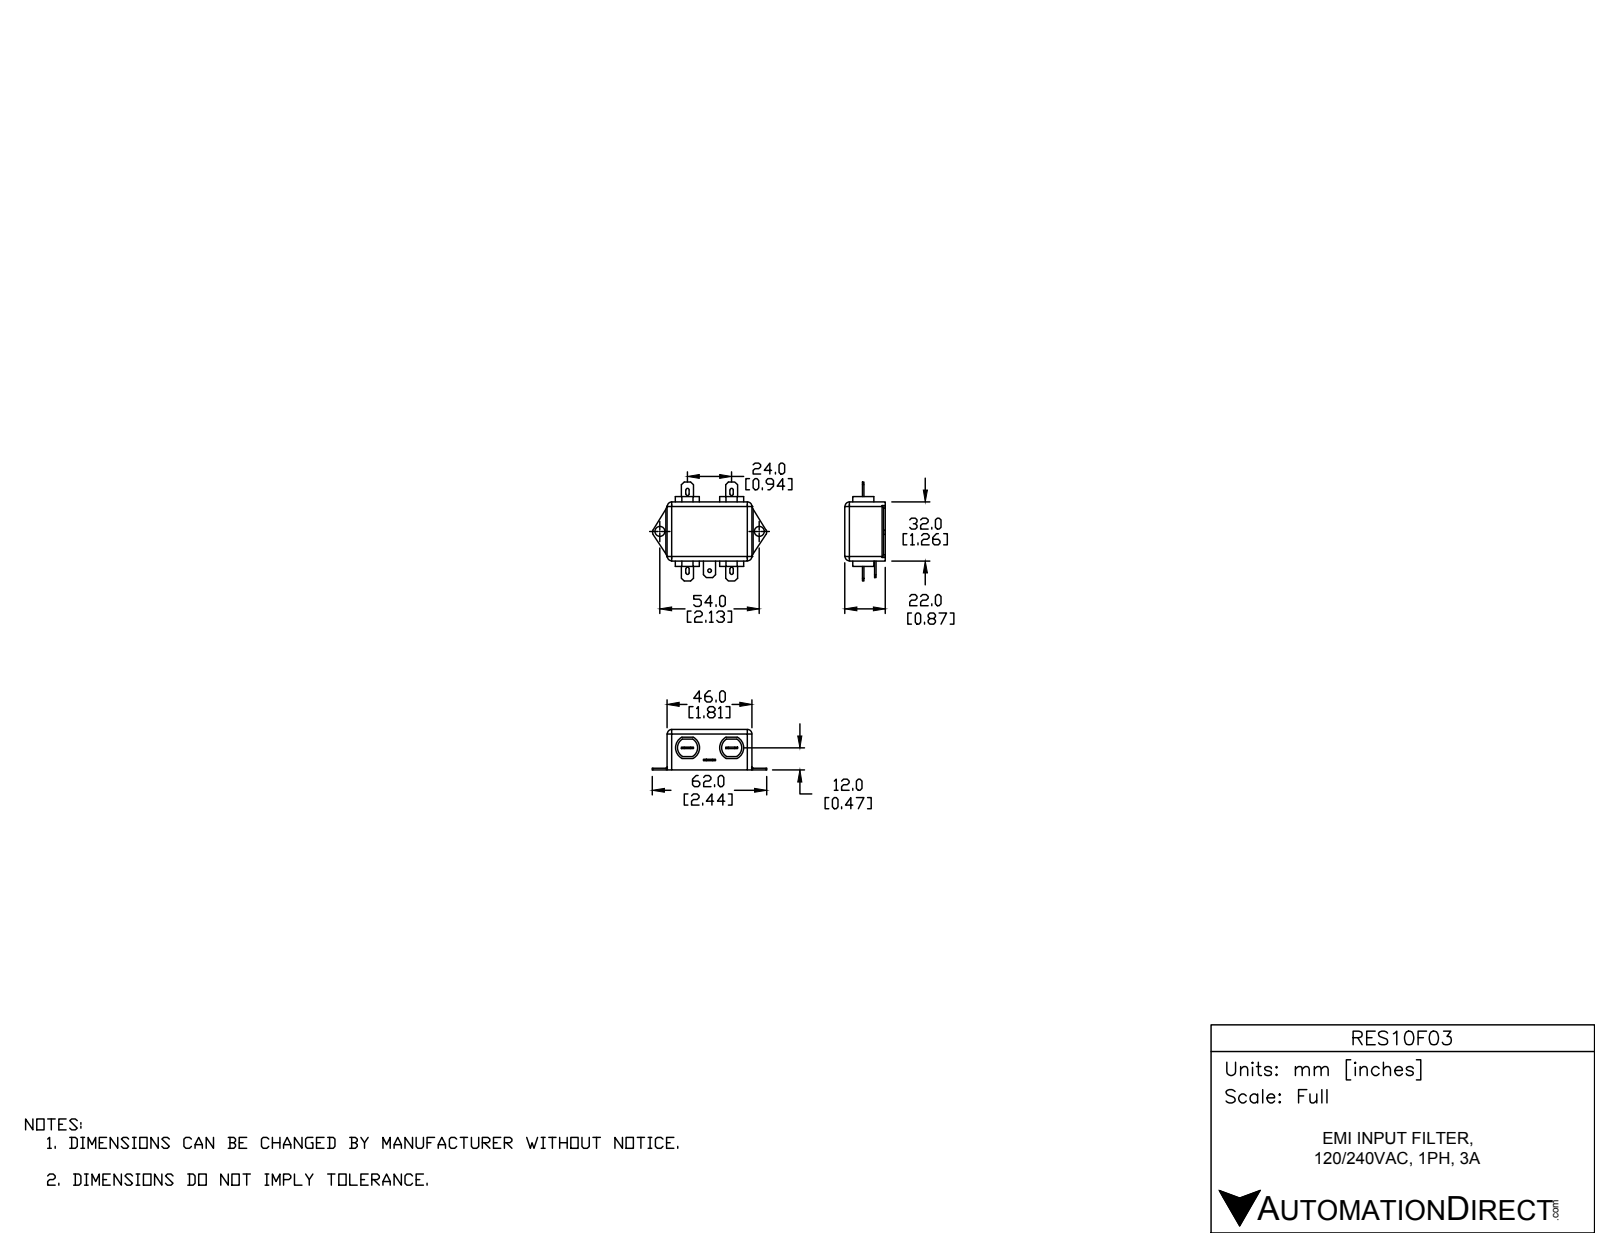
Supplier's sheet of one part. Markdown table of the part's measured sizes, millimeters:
| quantity | value |
| --- | --- |
| part name | RES10F03 |
| STEP written by | SolidWorks 2015 (AUTOMOTIVE_DESIGN) |
| units | millimeters |
| bodies | 1 solid, 137 faces (79 planar, 54 cylindrical, 4 other) |
| overall size | 61.3 × 56.1 × 22 |
| volume | 35 744 mm³ |
| surface area | 8 153 mm² |
| round holes (diameter × count) | 5.3 × 2, 2 × 1 |
| partial cylindrical surfaces (radius × count) | 2.5 × 10, 0.9 × 8, 0.75 × 2, 5.5 × 2, 6.5 × 2 |
| main face-to-face distances | 22, 34.3, 46, 1.4, 35.7, 0.8, 1, 11.6, 12.4, 10.4 |
| hole center spacings | 35.11, 54 |
